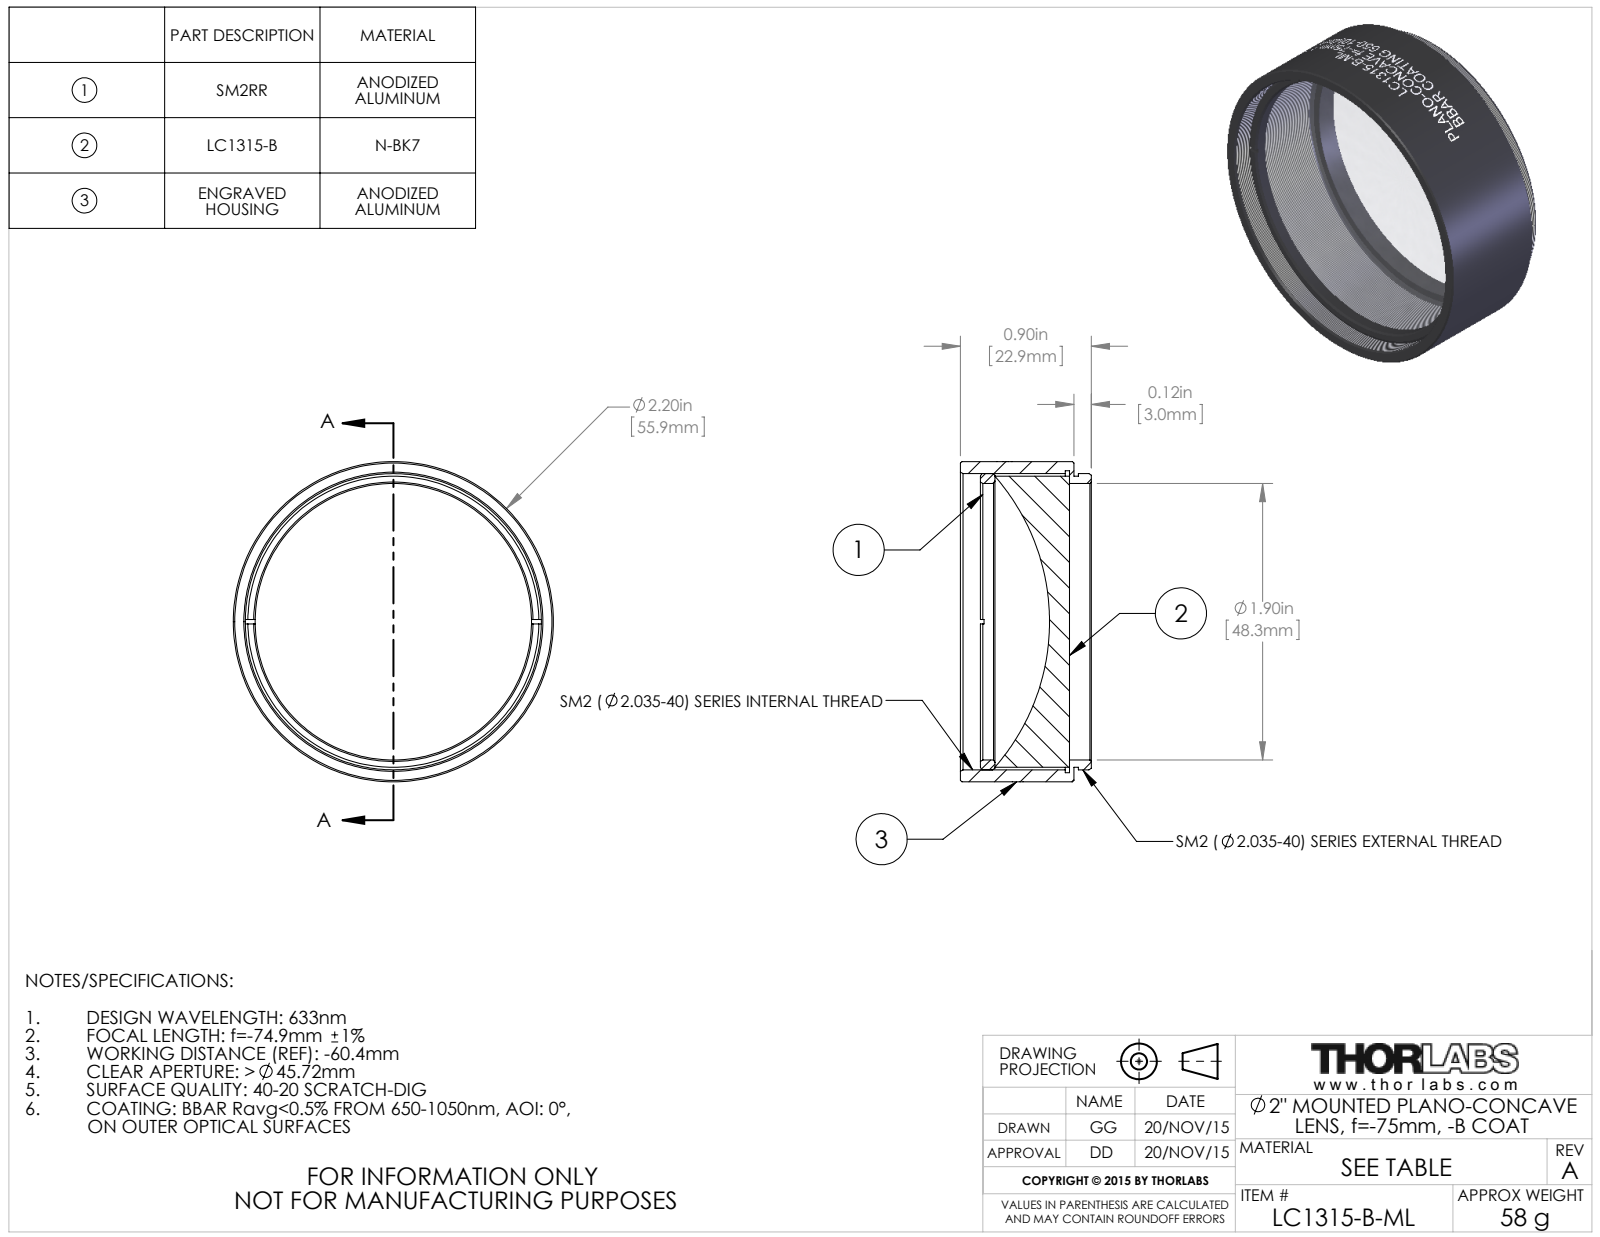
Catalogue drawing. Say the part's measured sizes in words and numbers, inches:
The part is named "TTN045326-E0W". Its 3-D file was written by "SolidWorks 2014 (CONFIG_CONTROL_DESIGN)". It is 3 solids with 145 faces: 16 planar, 107 cylindrical and 22 other. Overall it measures 2.2 by 2.2 by 0.9 inches. Its volume is 1.516 cubic inches and its surface area 25.9 square inches. Round holes: 1 of diameter 1.9, 1 of diameter 2.075. Round bosses or shafts: 1 of diameter 2.2, 1 of diameter 2.035, 1 of diameter 2, 1 of diameter 1.999. The main face-to-face distances are 0.03, 0.78, 0.75, 0.12, 0.15, 0.9, 0.663, 0.543, 0.513, 0.237.
